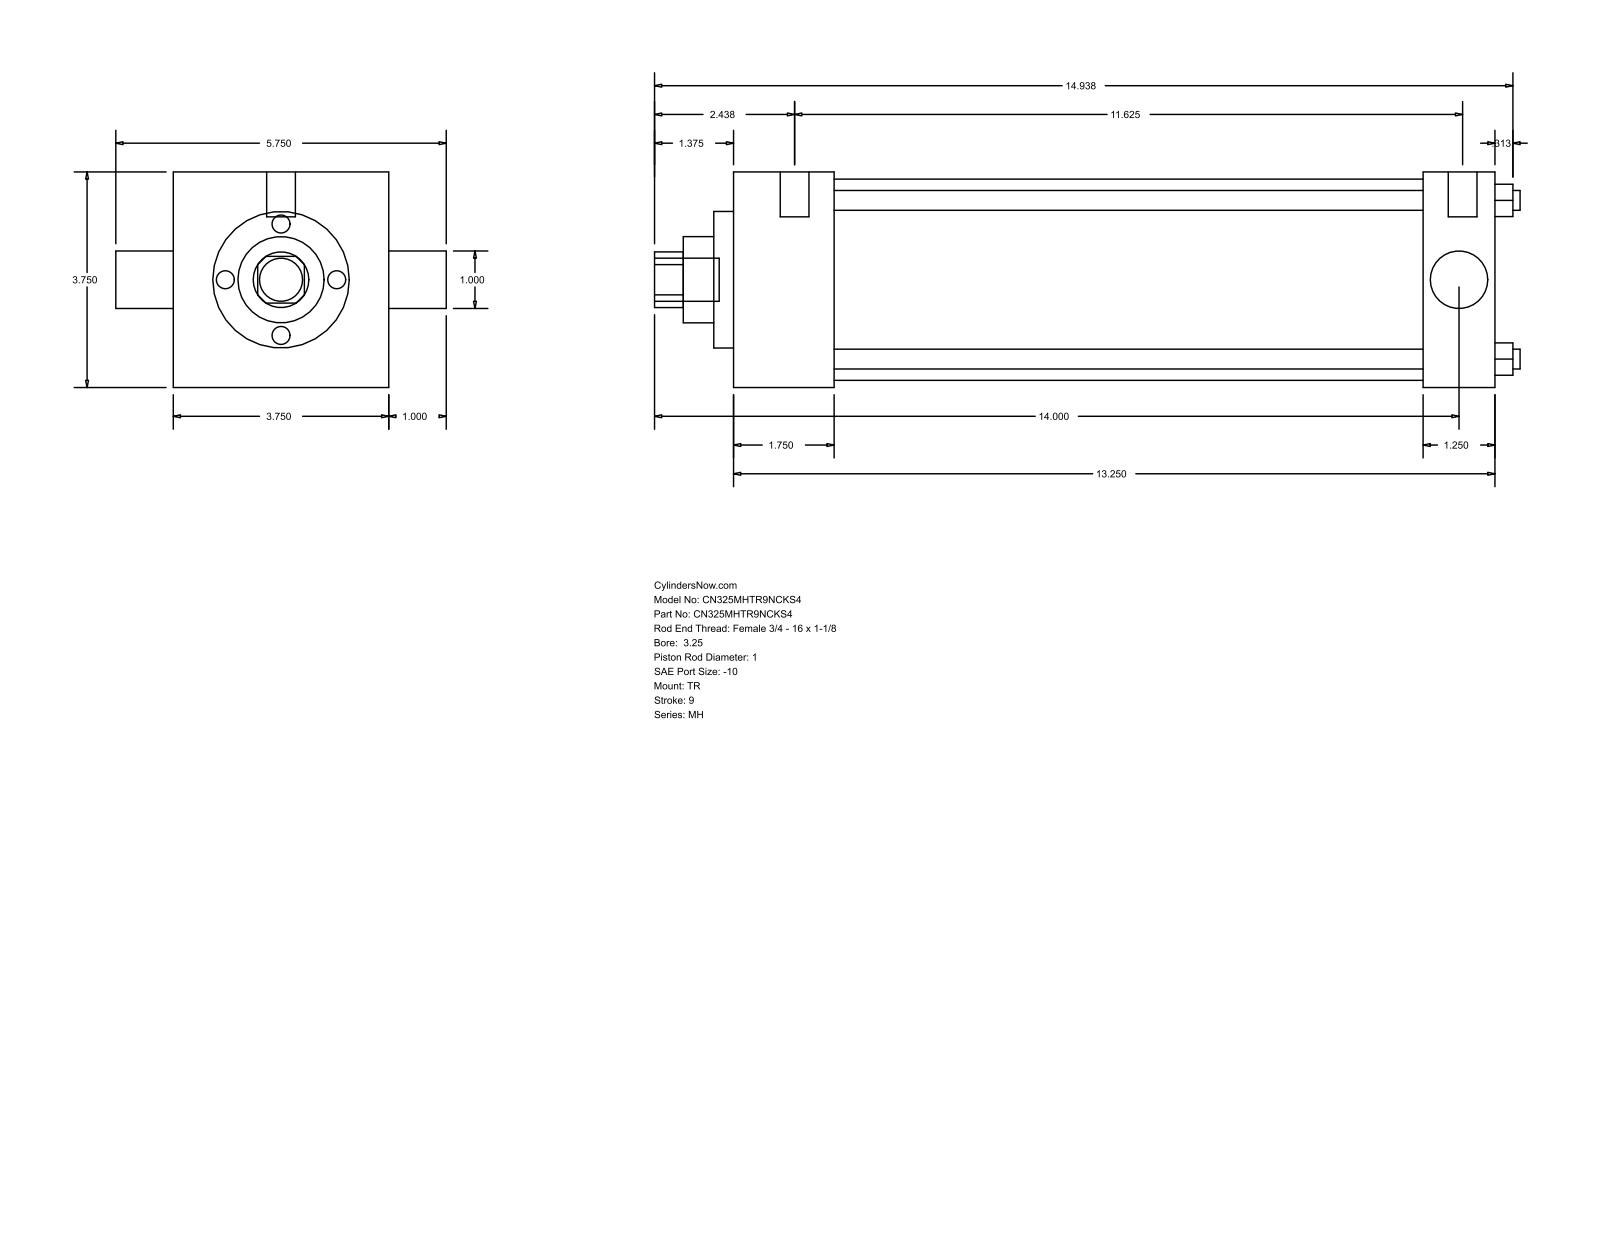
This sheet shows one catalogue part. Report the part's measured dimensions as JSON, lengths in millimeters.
{"part_name": "MH_TR__0325_1", "step_written_by": "GSSL Pune (CONFIG_CONTROL_DESIGN)", "units": "millimeters", "bodies": {"solids": 0, "faces": 86, "planar": 61, "cylindrical": 25, "other": 0}, "overall_size": [382.59, 146.05, 95.25], "round_holes": [[8.76, 4], [25.4, 2], [38.1, 1], [60.33, 1], [88.9, 1]], "round_bosses_or_shafts": [[5.56, 3], [12.7, 2], [19.05, 1]], "partial_cylinders_radius": [[12.29, 1]], "face_to_face_distances": [95.24, 336.56, 44.46, 304.81, 260.35, 292.1, 31.75, 8.73, 53.19, 313.54], "hole_center_spacings": [49.57, 70.1, 99.14]}
